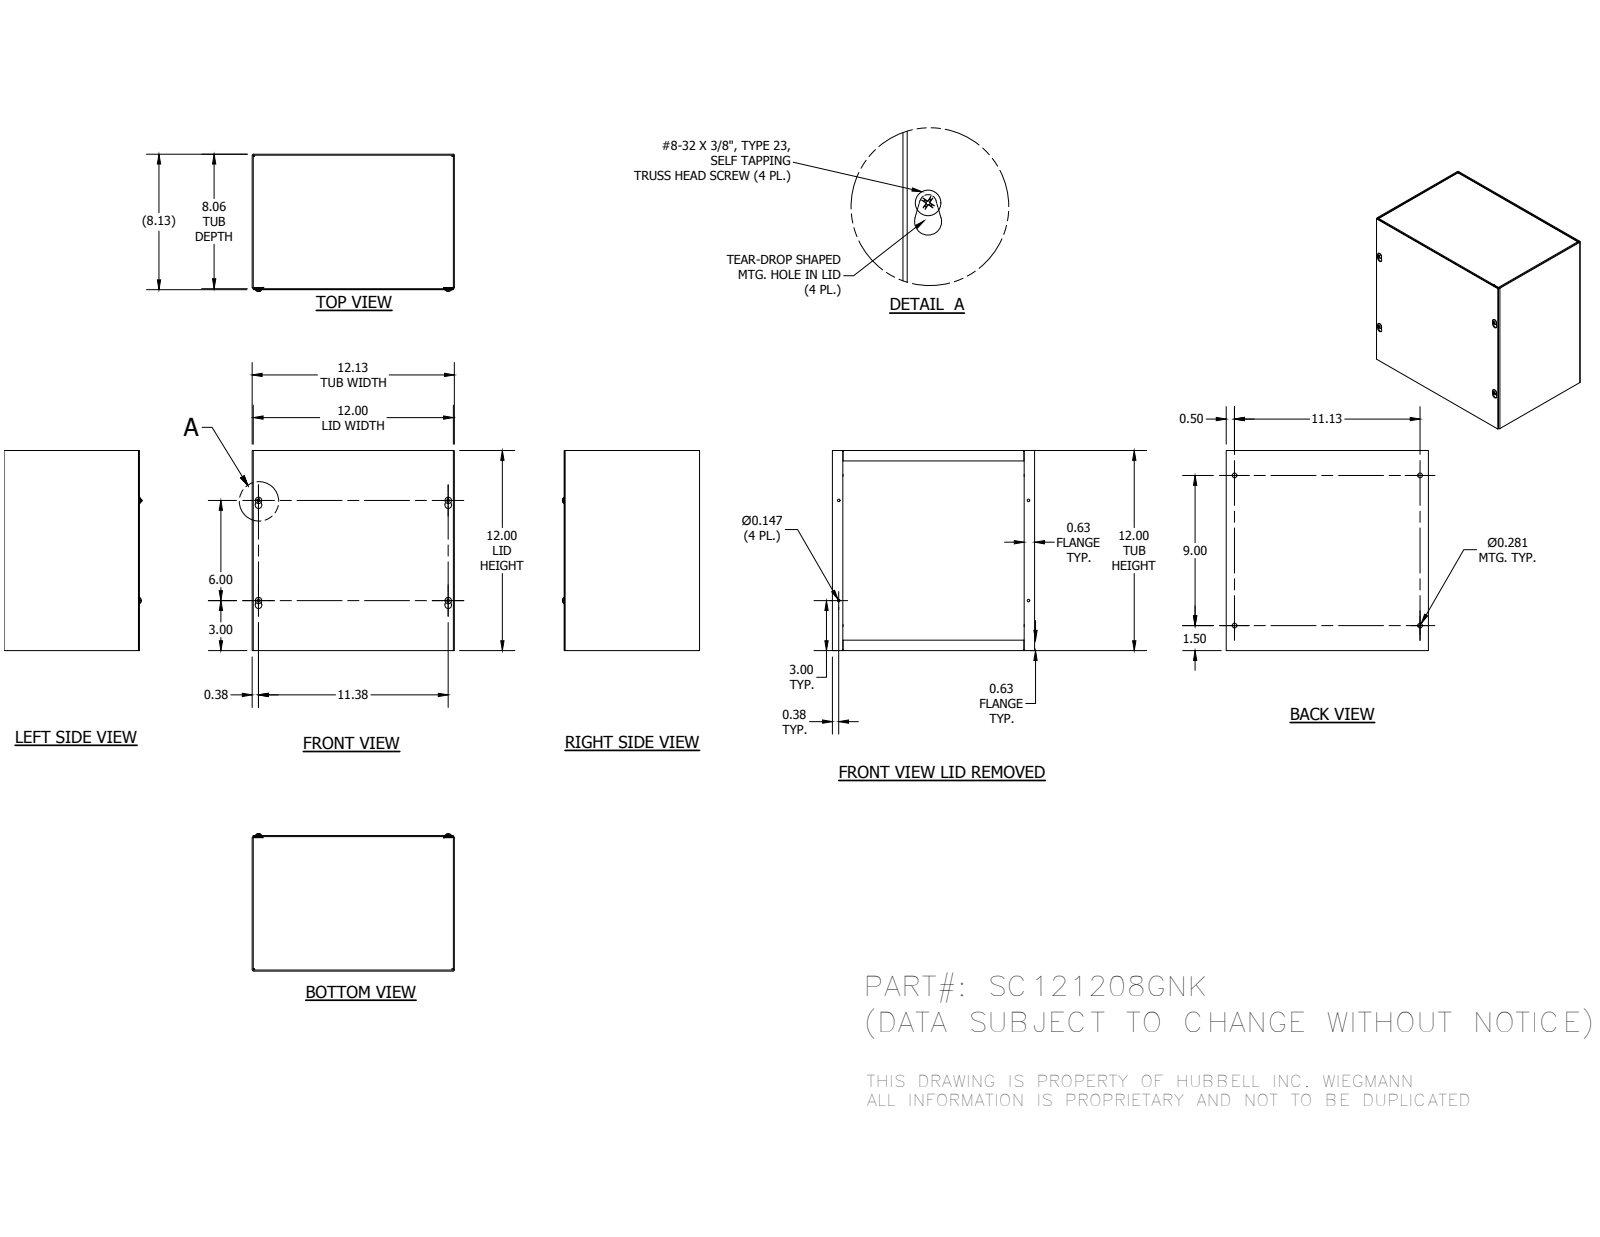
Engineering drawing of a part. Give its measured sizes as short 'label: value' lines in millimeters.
name: SC121208GNKBLR; SC1208GNKTB; SC1212GLPA; 34056 (+1 more)
written by: Autodesk Inventor 2014 (AUTOMOTIVE_DESIGN)
unit: mm
bodies: 8 solids, 268 faces (152 planar, 48 cylindrical, 68 other)
size: 307.98 × 304.8 × 208.92
volume: 744 919 mm³; area: 947 935 mm²
holes: 4× ⌀3.73, 4× ⌀7.14
bosses: 4× ⌀9.75, 4× ⌀4.17
rounds: 12× R0.4, 12× R1.98, 4× R3.17, 4× R5.16
face distances: 1.59, 304.8, 303.21, 203.2, 306.39, 1.58, 204.78, 204.79, 206.37, 301.62
hole spacings: 38.23, 190.53, 288.28, 343.43, 152.4, 228.6, 282.58, 288.92
